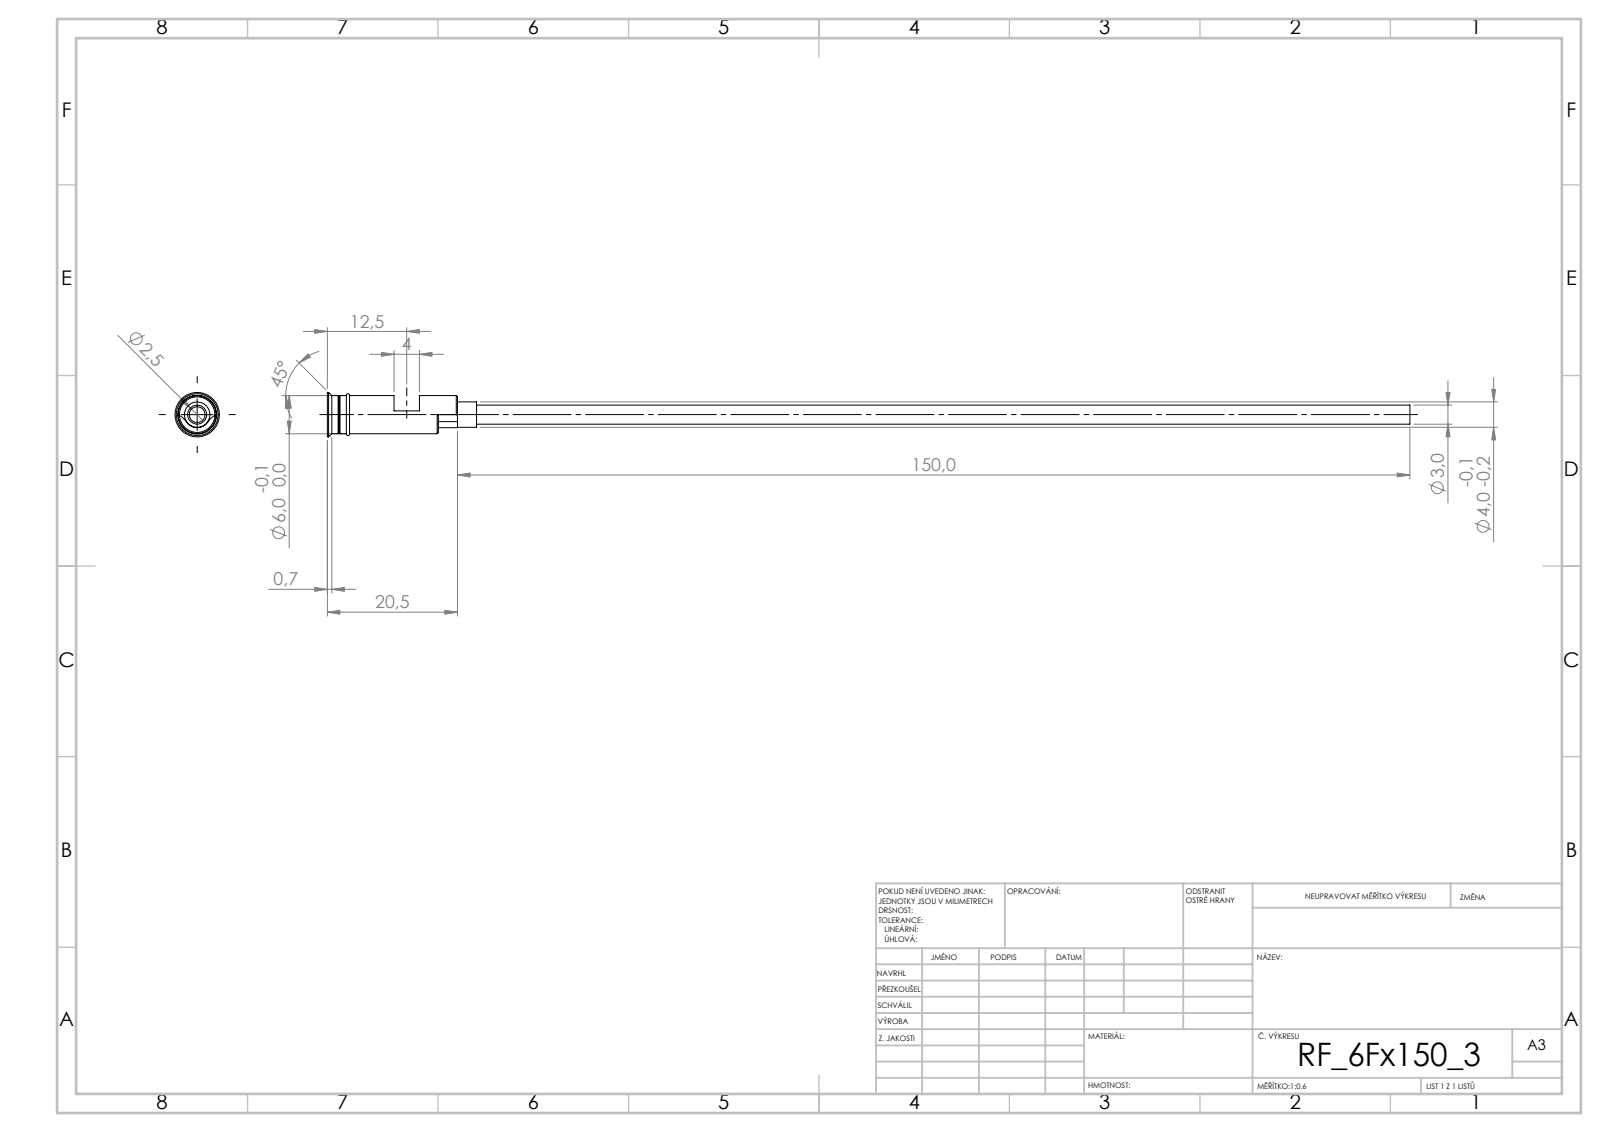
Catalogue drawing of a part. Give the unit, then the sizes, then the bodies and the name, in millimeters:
Units: millimetres
Overall size (bounding box): 170.5 × 7 × 7
Round holes (diameter × count): ⌀2.5 ×1
Round bosses / shafts (diameter × count): ⌀7 ×1, ⌀6 ×1, ⌀5.8 ×1, ⌀4 ×1, ⌀3 ×1
Partial cylindrical surfaces — rounded edges, fillets, slot ends (radius × count): R3 ×2, R2.05 ×1
Main face-to-face distances: 3, 10.5, 6, 14.5, 2, 4, 20.5, 10, 7, 17.5
Volume: 811 mm³ · Surface area: 3 145 mm²
Bodies: 1 solid, 55 faces (24 planar, 19 cylindrical, 12 other)
STEP written by: SolidWorks 2019 (CONFIG_CONTROL_DESIGN)
